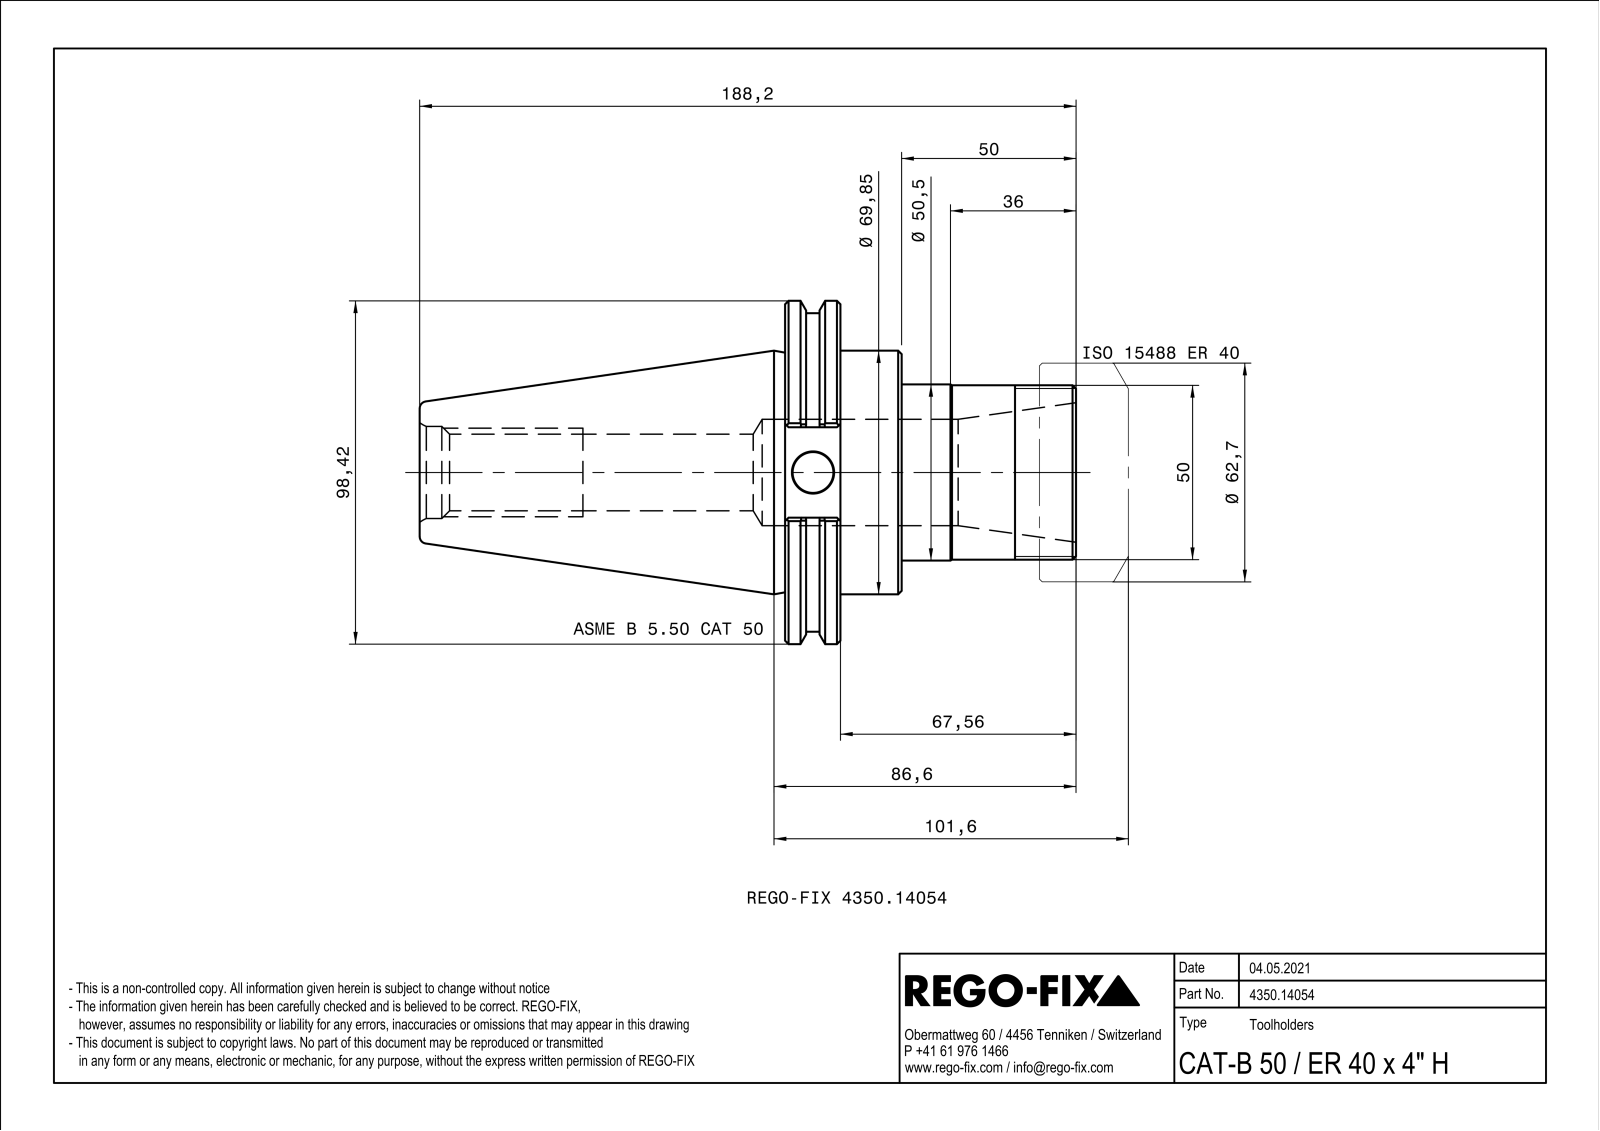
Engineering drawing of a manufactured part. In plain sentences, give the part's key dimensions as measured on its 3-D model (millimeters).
The part is named "NOCUT". Its 3-D file was written by "SIEMENS PLM Software Solid Edge ST10 (AUTOMOTIVE_DESIGN)". It is 1 solid with 118 faces: 36 planar, 41 cylindrical and 41 other. Overall it measures 188.2 by 98.42 by 94.39 millimeters. Its volume is 415 498 cubic millimeters and its surface area 63 221 square millimeters. Round holes: 2 of diameter 3.24, 2 of diameter 3.9, 1 of diameter 11.7, 1 of diameter 21.96, 1 of diameter 21.96, 1 of diameter 26.4, 1 of diameter 30.5. Round bosses or shafts: 1 of diameter 98.42, 1 of diameter 91.3, 1 of diameter 69.85, 1 of diameter 50.5, 1 of diameter 50. Partial cylindrical surfaces (rounded edges, fillets, slot ends): 12 of radius 0.5. The main face-to-face distances are 15.87, 17.56, 33.43, 50, 67.56, 83.43, 188.2, 138.2, 120.64, 104.77.
